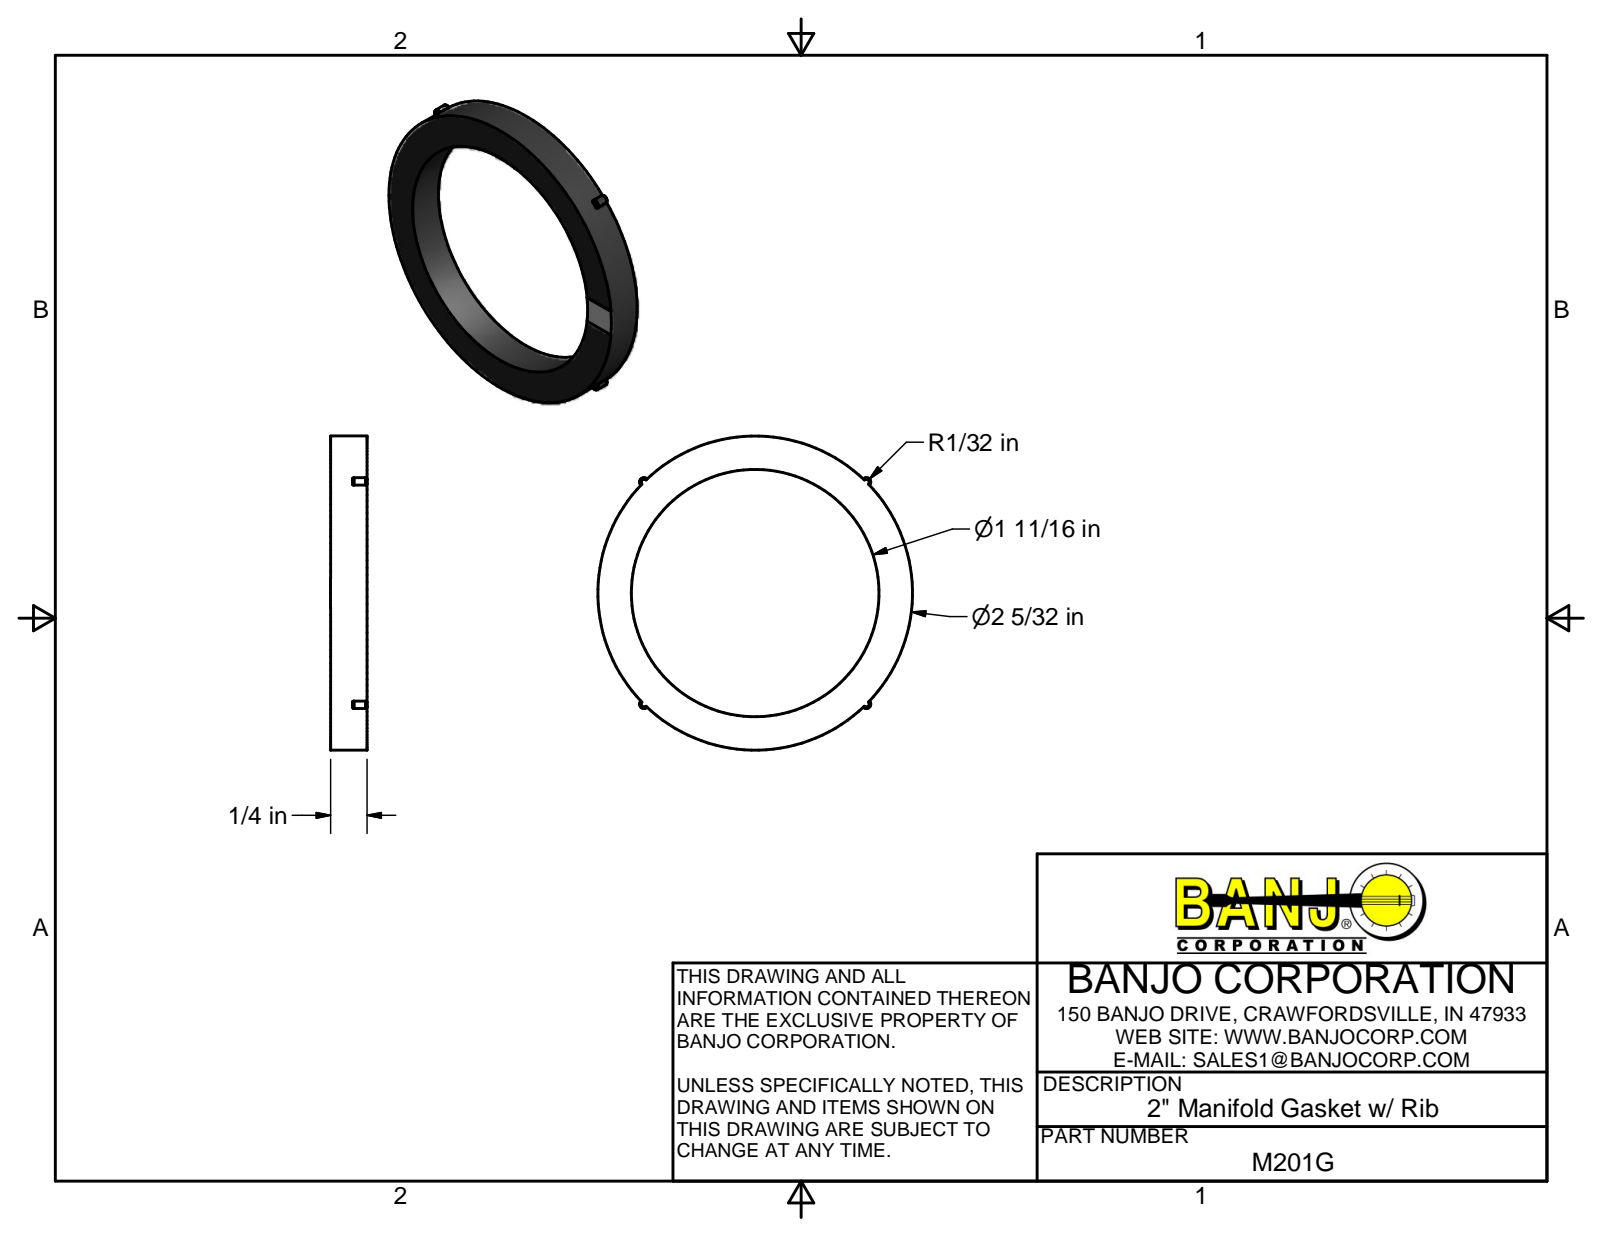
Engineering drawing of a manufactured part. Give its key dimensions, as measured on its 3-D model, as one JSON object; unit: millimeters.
{"part_name": "M201G", "step_written_by": "Autodesk Inventor 2011 (AUTOMOTIVE_DESIGN)", "units": "millimeters", "bodies": {"solids": 1, "faces": 23, "planar": 9, "cylindrical": 6, "other": 8}, "overall_size": [54.9, 54.9, 6.4], "volume_mm3": 5720, "surface_area_mm2": 3770, "round_holes": [[43.2, 1]], "round_bosses_or_shafts": [[54.9, 1]], "partial_cylinders_radius": [[0.8, 4]], "face_to_face_distances": [6.4, 6.4, 3.8, 3.8, 2.5, 5.1]}
